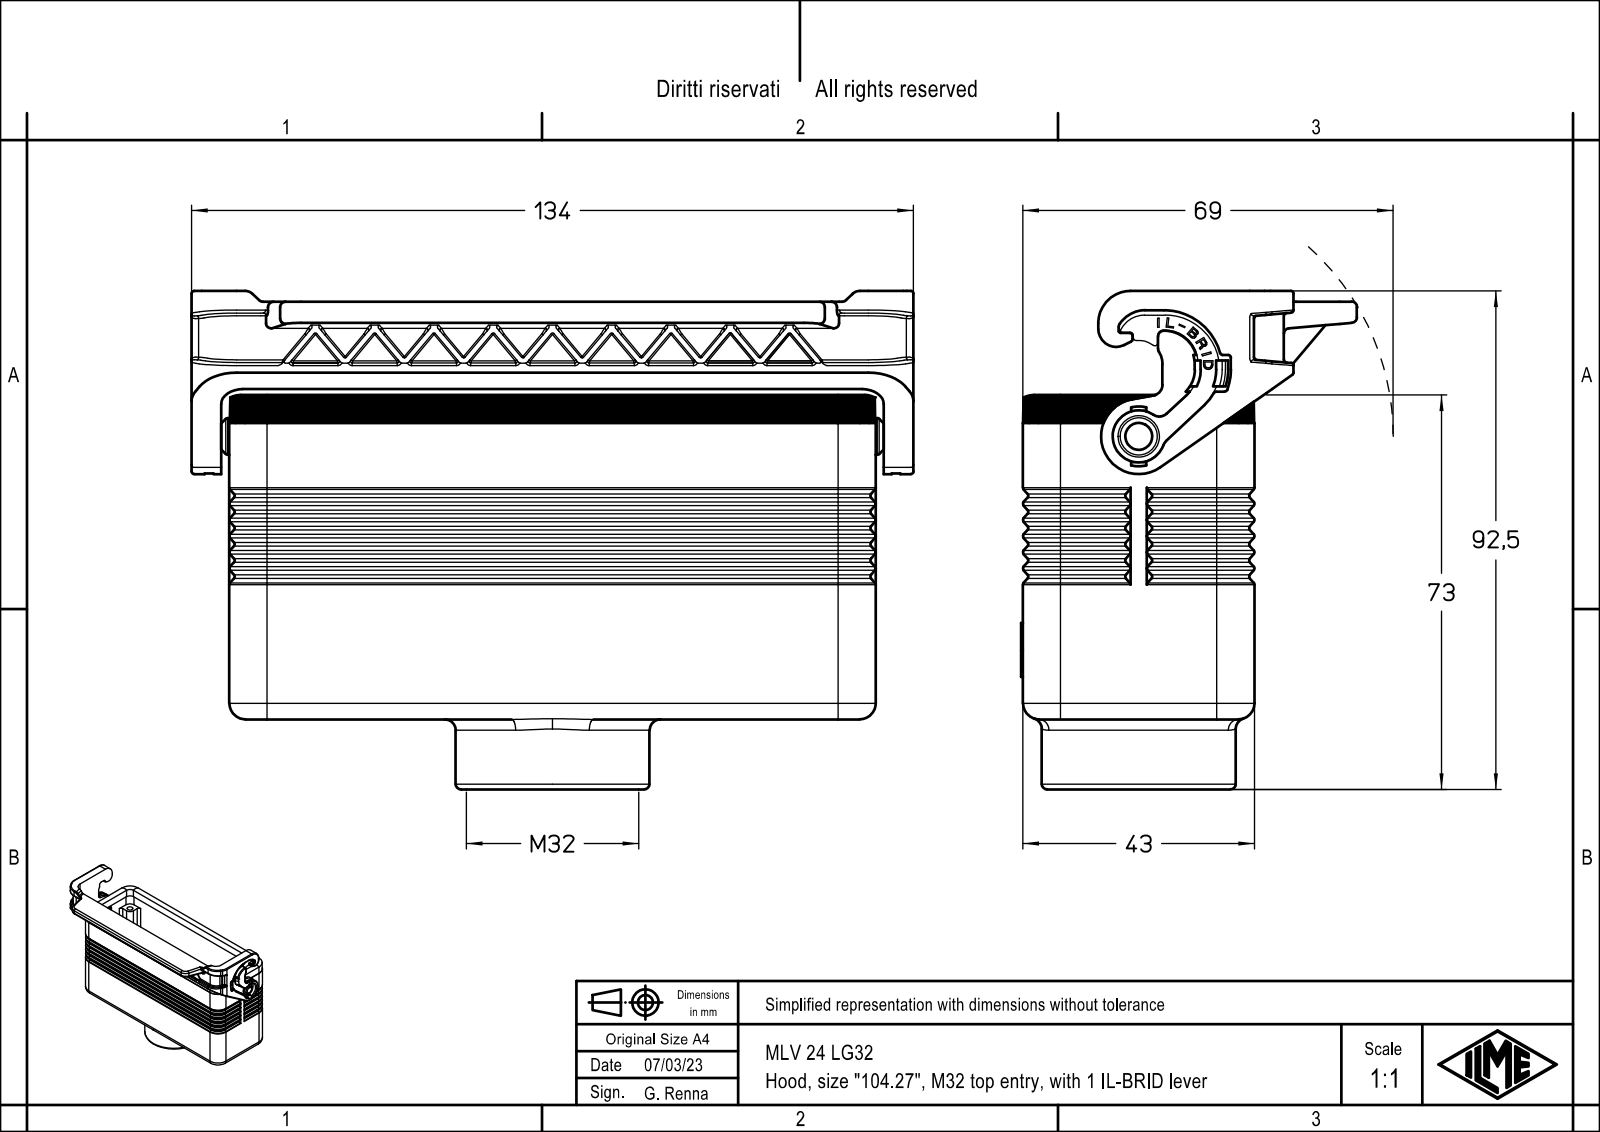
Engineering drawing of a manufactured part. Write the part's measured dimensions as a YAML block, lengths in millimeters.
part_name: "MLV 24 LG32"
step_written_by: "Creo Elements/Direct Modeling 20.1B 02-Apr-2019 (C) Parametric Technology GmbH (AUTOMOTIVE_DESIGN)"
units: millimeters
bodies: {solids: 1, faces: 1308, planar: 747, cylindrical: 353, other: 208}
overall_size: [134, 92.5, 62.3]
volume: 103607
surface_area: 64354
round_holes:
  - {diameter: 3, count: 4}
  - {diameter: 3.5, count: 4}
  - {diameter: 3.25, count: 1}
  - {diameter: 5.4, count: 1}
  - {diameter: 7.7, count: 1}
  - {diameter: 28, count: 1}
  - {diameter: 30.6, count: 1}
round_bosses_or_shafts:
  - {diameter: 36, count: 1}
  - {diameter: 6.9, count: 1}
  - {diameter: 6.8, count: 1}
  - {diameter: 5.2, count: 1}
  - {diameter: 3.2, count: 1}
partial_cylinders:
  - {radius: 0.5, count: 55}
  - {radius: 0.1, count: 27}
  - {radius: 1, count: 16}
  - {radius: 0.2, count: 15}
  - {radius: 0.33, count: 15}
  - {radius: 3, count: 12}
  - {radius: 7, count: 10}
  - {radius: 1.5, count: 9}
face_to_face_distances: [3.5, 39.5, 36, 43, 2.8, 2, 4, 46.25, 3.25, 6.75]
hole_center_spacings: [53.72, 27, 104, 107.45]
